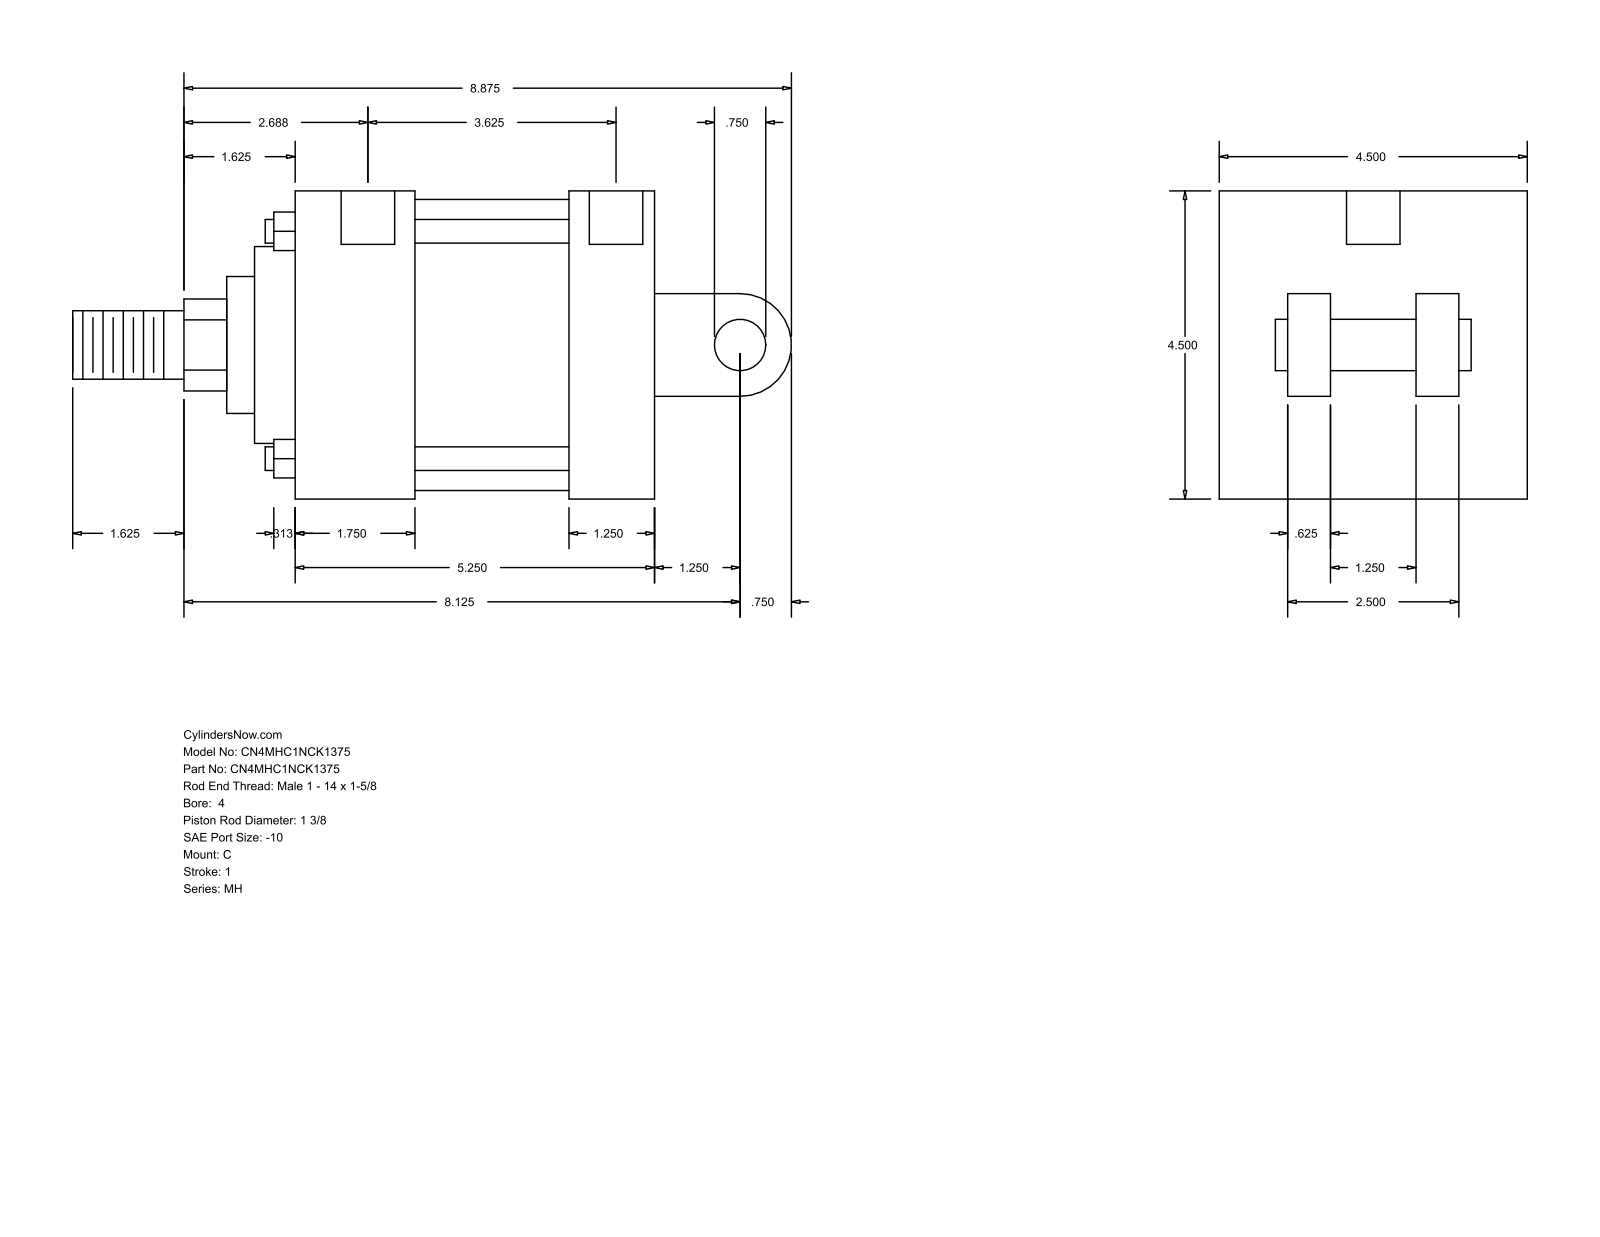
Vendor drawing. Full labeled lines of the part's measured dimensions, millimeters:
Part name (STEP PRODUCT): MH_C__0400_1.375
STEP written by: GSSL Pune (CONFIG_CONTROL_DESIGN)
Units: millimetres
Bodies: 0 solids, 101 faces (71 planar, 30 cylindrical, 0 other)
Overall size (bounding box): 266.7 × 114.3 × 114.3
Round holes (diameter × count): ⌀8.73 ×4, ⌀19.84 ×2
Round bosses / shafts (diameter × count): ⌀8.76 ×4, ⌀107.95 ×1, ⌀73.03 ×1, ⌀50.8 ×1, ⌀34.92 ×1, ⌀25.4 ×1, ⌀19.05 ×1
Partial cylindrical surfaces — rounded edges, fillets, slot ends (radius × count): R17.06 ×1, R19.05 ×1
Main face-to-face distances: 114.3, 133.35, 88.9, 44.45, 101.61, 57.16, 31.74, 41.27, 73.03, 38.1
Hole centre spacings: 1.59, 93.67, 95.26, 92.08
